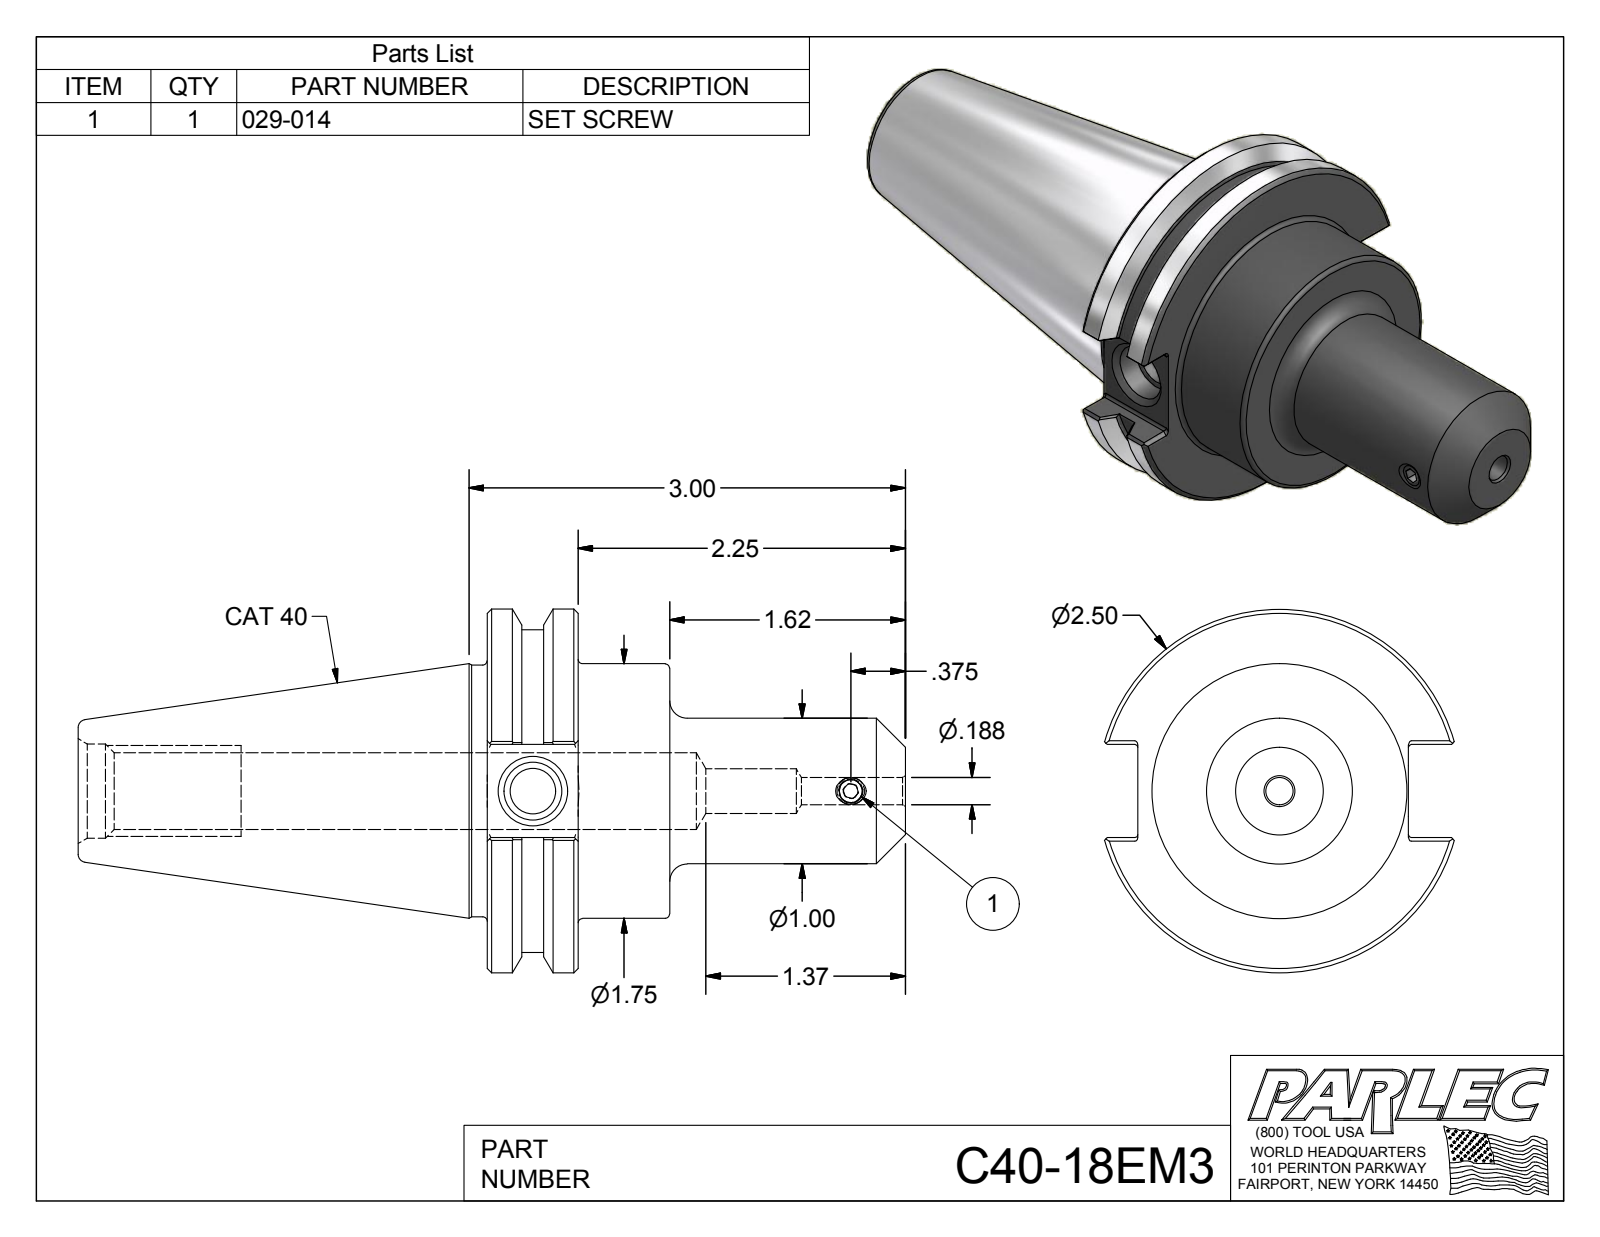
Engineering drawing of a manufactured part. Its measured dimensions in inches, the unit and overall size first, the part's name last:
Units: inches
Overall size (bounding box): 5.687 × 2.5 × 2.406
Round holes (diameter × count): ⌀0.156 ×1, ⌀0.187 ×1, ⌀0.307 ×1, ⌀0.315 ×1, ⌀0.399 ×1, ⌀0.527 ×1, ⌀0.648 ×1
Round bosses / shafts (diameter × count): ⌀2.5 ×1, ⌀2.219 ×1, ⌀1.75 ×1, ⌀1.73 ×1, ⌀1 ×1, ⌀0.19 ×1
Partial cylindrical surfaces — rounded edges, fillets, slot ends (radius × count): R0.02 ×12
Main face-to-face distances: 0.625, 1.255, 0.63, 2.875, 2.25, 1.62, 0.64, 1.86, 2.812, 3.437
Hole centre spacings: 2.185
Volume: 8.61 in³ · Surface area: 42.27 in²
Bodies: 2 solids, 104 faces (41 planar, 29 cylindrical, 34 other)
Part name (STEP PRODUCT): C40-18EM3; C40-18EM3-1; 029-014
STEP written by: Autodesk Inventor 2012 (AUTOMOTIVE_DESIGN)
